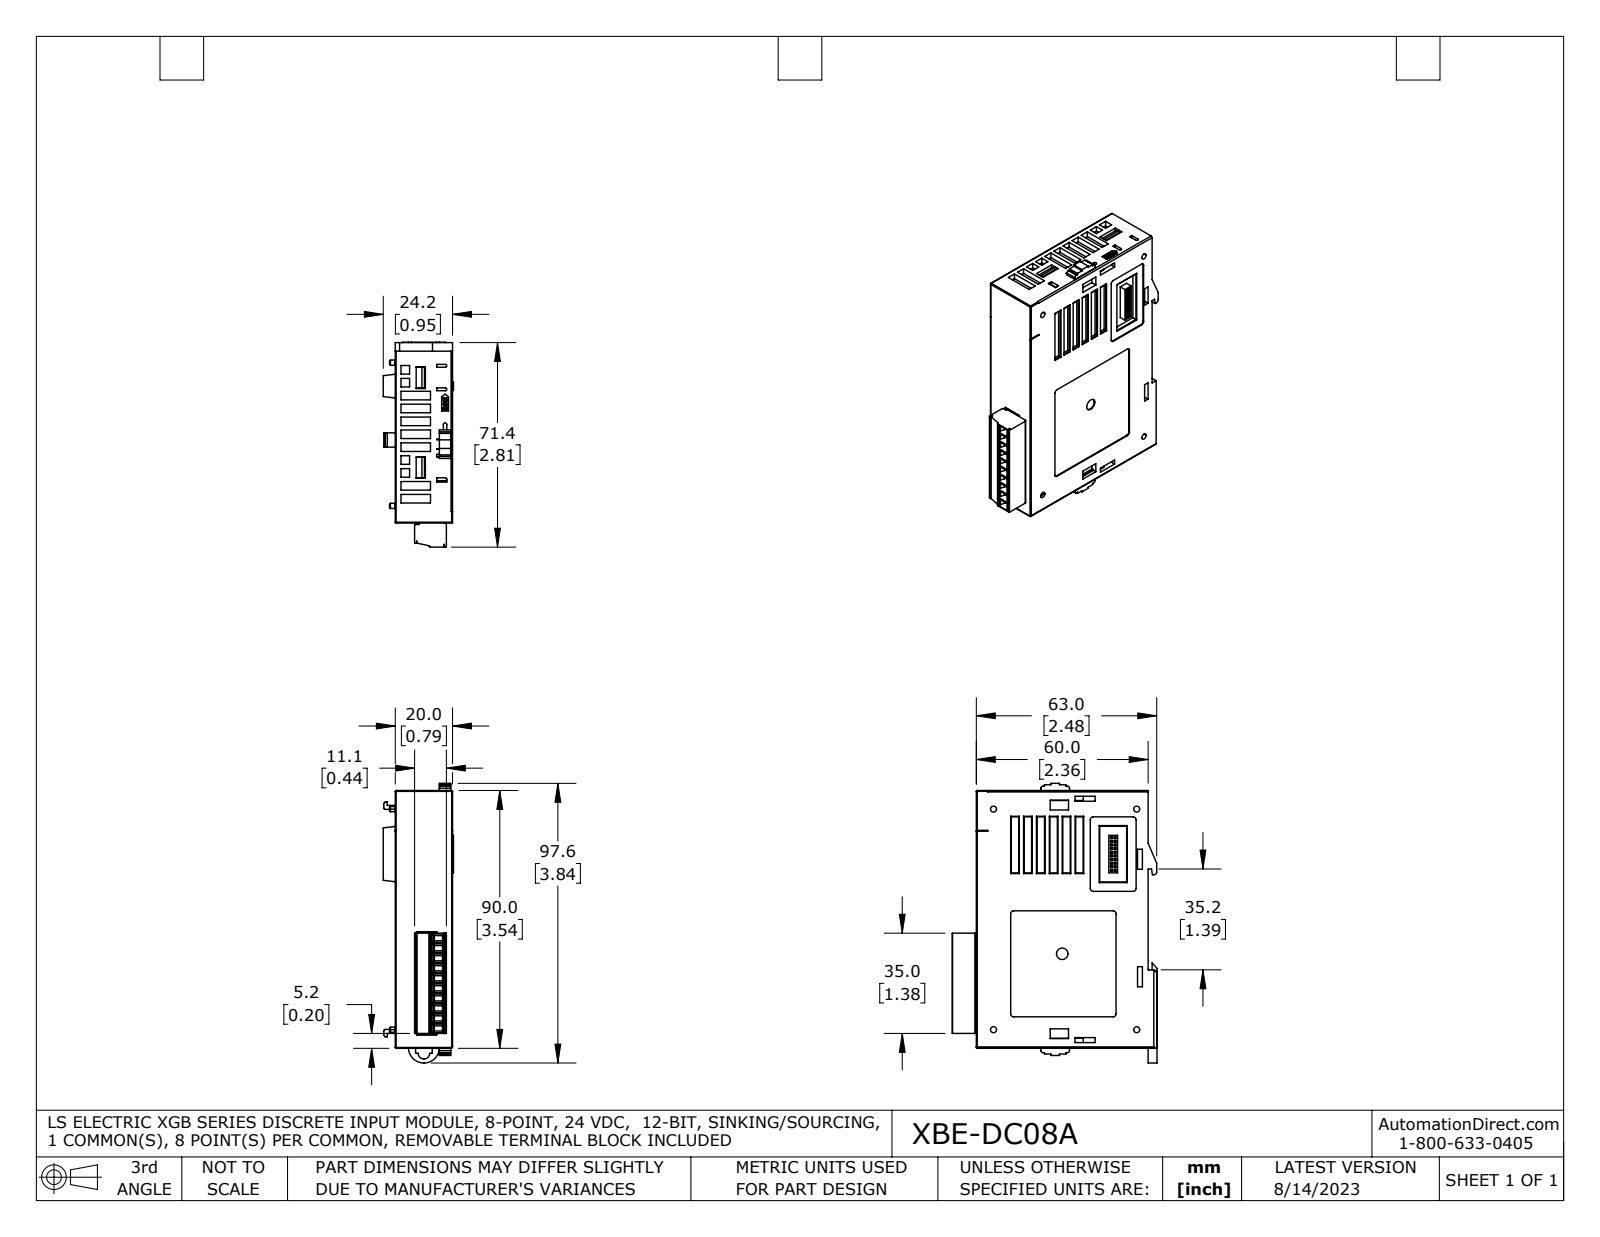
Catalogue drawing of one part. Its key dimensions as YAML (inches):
part_name: "XBE-DC08A nc din clip 6 bad faces cut1 coord fxt"
step_written_by: "SolidWorks 2021 (AUTOMOTIVE_DESIGN)"
units: inches
bodies: {solids: 1, faces: 2347, planar: 1755, cylindrical: 404, other: 188}
overall_size: [3.844, 2.815, 0.966]
volume: 6.571
surface_area: 45.24
round_holes:
  - {diameter: 0.108, count: 10}
  - {diameter: 0.116, count: 10}
  - {diameter: 0.083, count: 4}
  - {diameter: 0.071, count: 2}
  - {diameter: 0.157, count: 1}
round_bosses_or_shafts:
  - {diameter: 0.11, count: 10}
  - {diameter: 0.071, count: 6}
partial_cylinders:
  - {radius: 0.008, count: 42}
  - {radius: 0.004, count: 40}
  - {radius: 0.012, count: 38}
  - {radius: 0.02, count: 21}
  - {radius: 0.039, count: 11}
  - {radius: 0.062, count: 10}
  - {radius: 0.071, count: 10}
  - {radius: 0.031, count: 6}
face_to_face_distances: [0.787, 0.079, 0.039, 0.776, 0.709, 2.362, 0.748, 0.669, 0.067, 0.031]
hole_center_spacings: [0.138, 0.276, 0.413, 0.551, 0.689, 0.827, 0.965, 0.539]
